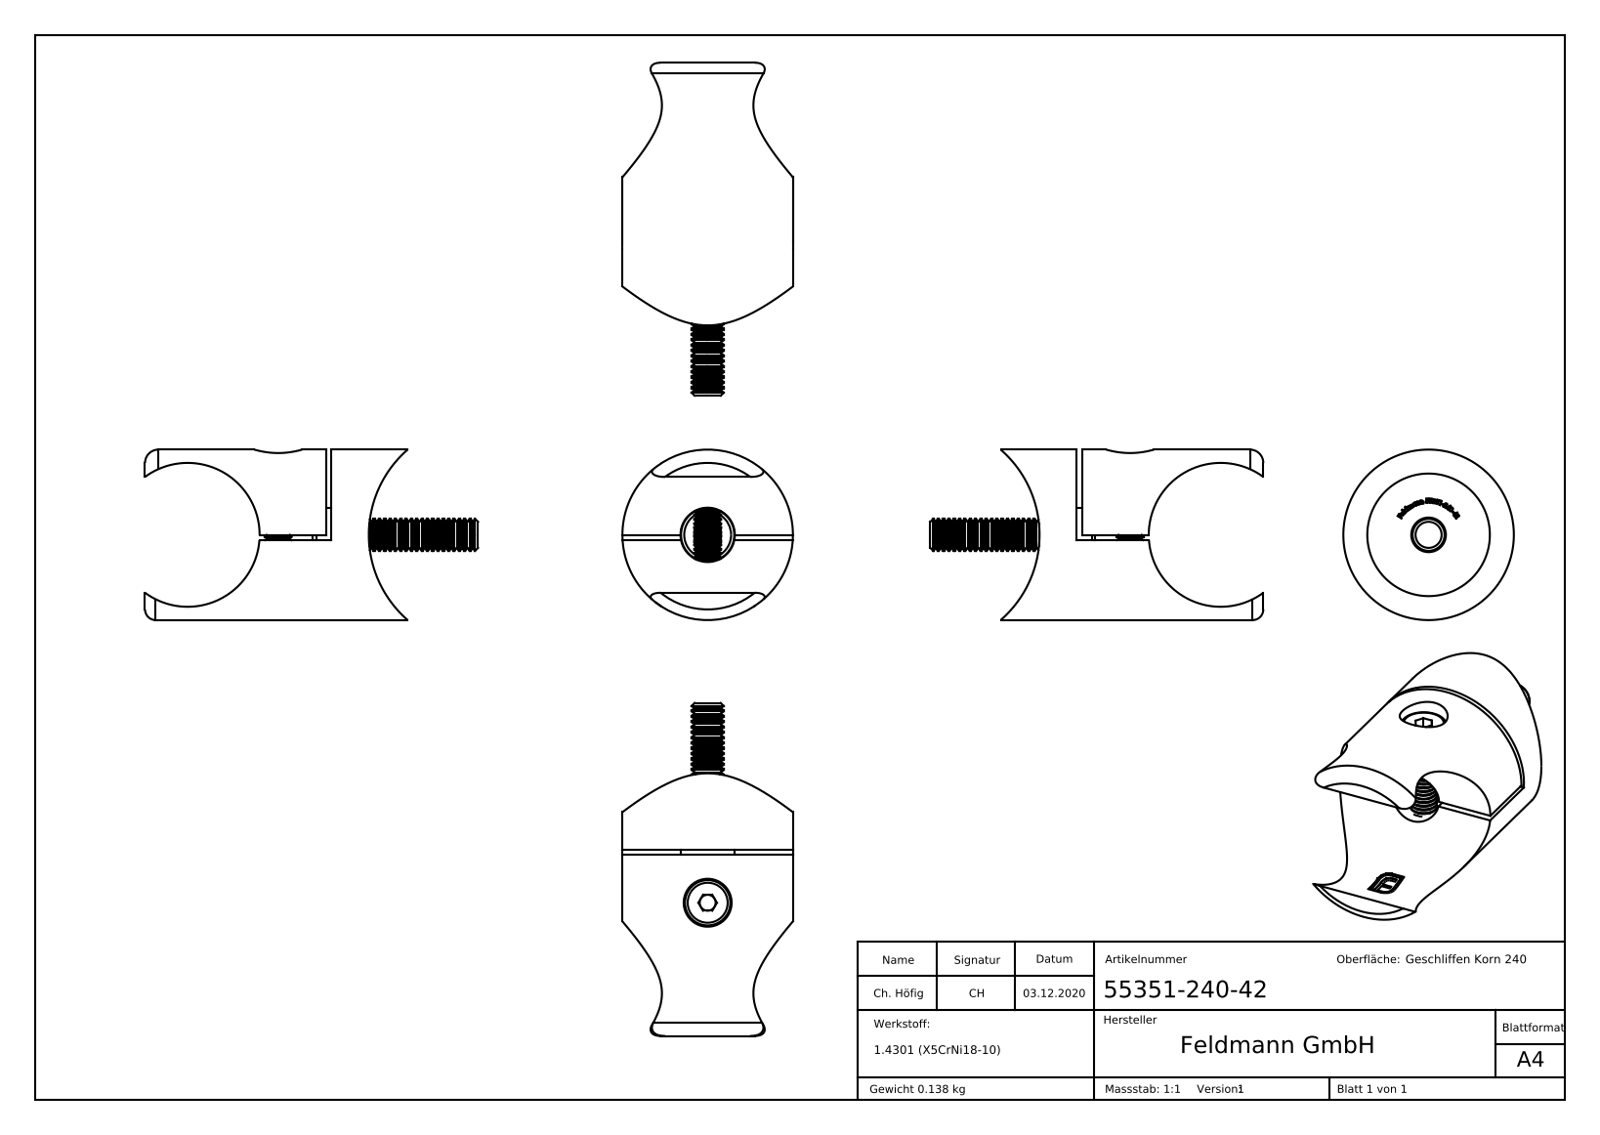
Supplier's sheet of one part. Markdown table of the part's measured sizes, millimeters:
| quantity | value |
| --- | --- |
| part name | 55351-240-42 Teil2_55351-240-42 Teil2; socket head cap screw_din; 55351-240-42 Teil2; 55351-240-42 Teil1 (+5 more) |
| STEP written by | SolidWorks 2018 (CONFIG_CONTROL_DESIGN) |
| units | millimeters |
| bodies | 4 solids, 653 faces (214 planar, 116 cylindrical, 323 other) |
| overall size | 62.5 × 32 × 32 |
| volume | 18 822 mm³ |
| surface area | 9 773 mm² |
| round holes (diameter × count) | 4.2 × 1, 5.5 × 1, 6.5 × 1, 9 × 1, 10.2 × 1, 23 × 1 |
| round bosses / shafts (diameter × count) | 32 × 1, 10 × 1, 8.5 × 1, 6 × 1, 5 × 1 |
| partial cylindrical surfaces (radius × count) | 13.5 × 1, 13.6 × 1, 21.2 × 1 |
| main face-to-face distances | 1, 6, 5, 2.5, 3.5, 11.5, 10.5, 40, 37.5, 35 |
